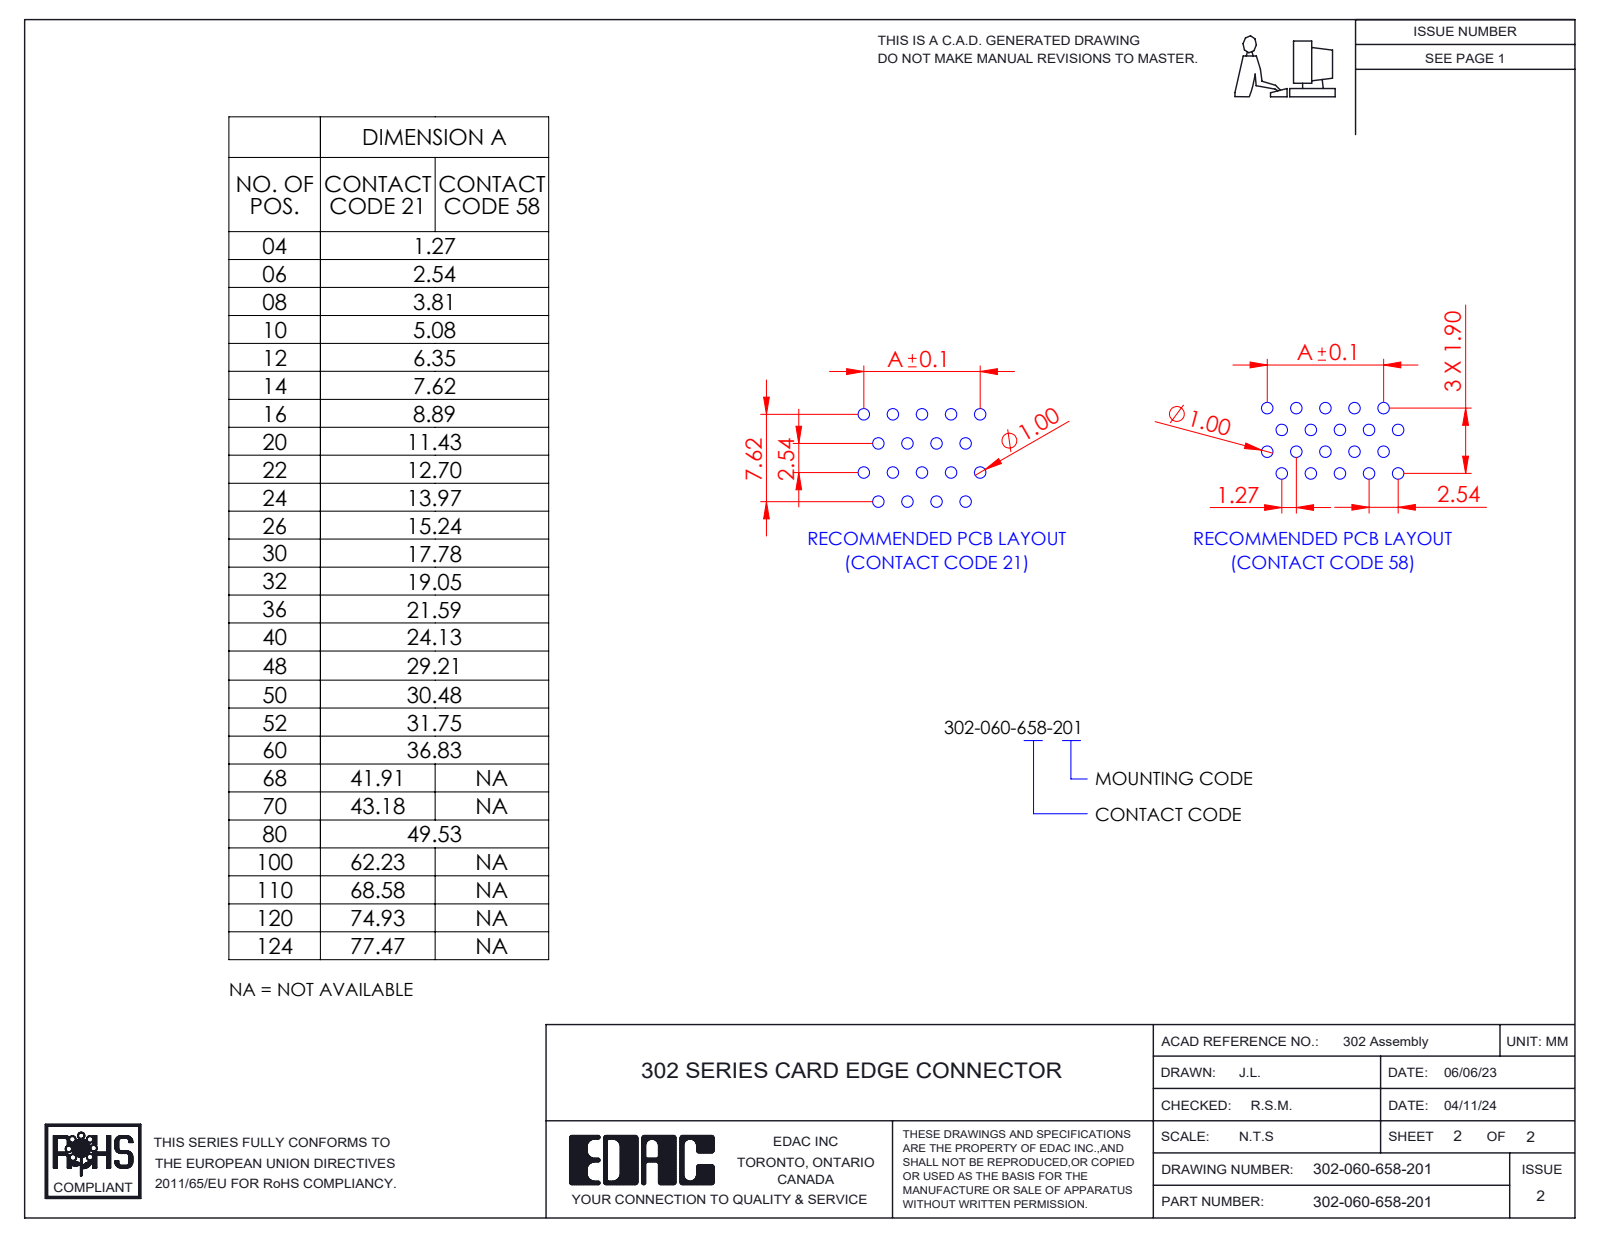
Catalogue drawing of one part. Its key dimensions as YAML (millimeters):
part_name: "Contact_302-290-X58-004; HSG_RA HSG; Contact_302-290-X58-002; Contact_302-290-X58-003 (+2 more)"
step_written_by: "SolidWorks 2023 (CONFIG_CONTROL_DESIGN)"
units: millimeters
bodies: {solids: 61, faces: 3181, planar: 2263, cylindrical: 794, other: 124}
overall_size: [44.2, 21.37, 11.68]
volume: 3970
surface_area: 10862
partial_cylinders:
  - {radius: 0.2, count: 68}
  - {radius: 0.25, count: 60}
  - {radius: 0.5, count: 4}
  - {radius: 2.03, count: 3}
  - {radius: 0.11, count: 2}
  - {radius: 0.4, count: 2}
  - {radius: 0.41, count: 2}
  - {radius: 0.8, count: 2}
face_to_face_distances: [8.88, 1.27, 2.54, 1.9, 3.81, 3.8, 7.62, 5.08, 6.35, 16.51]
